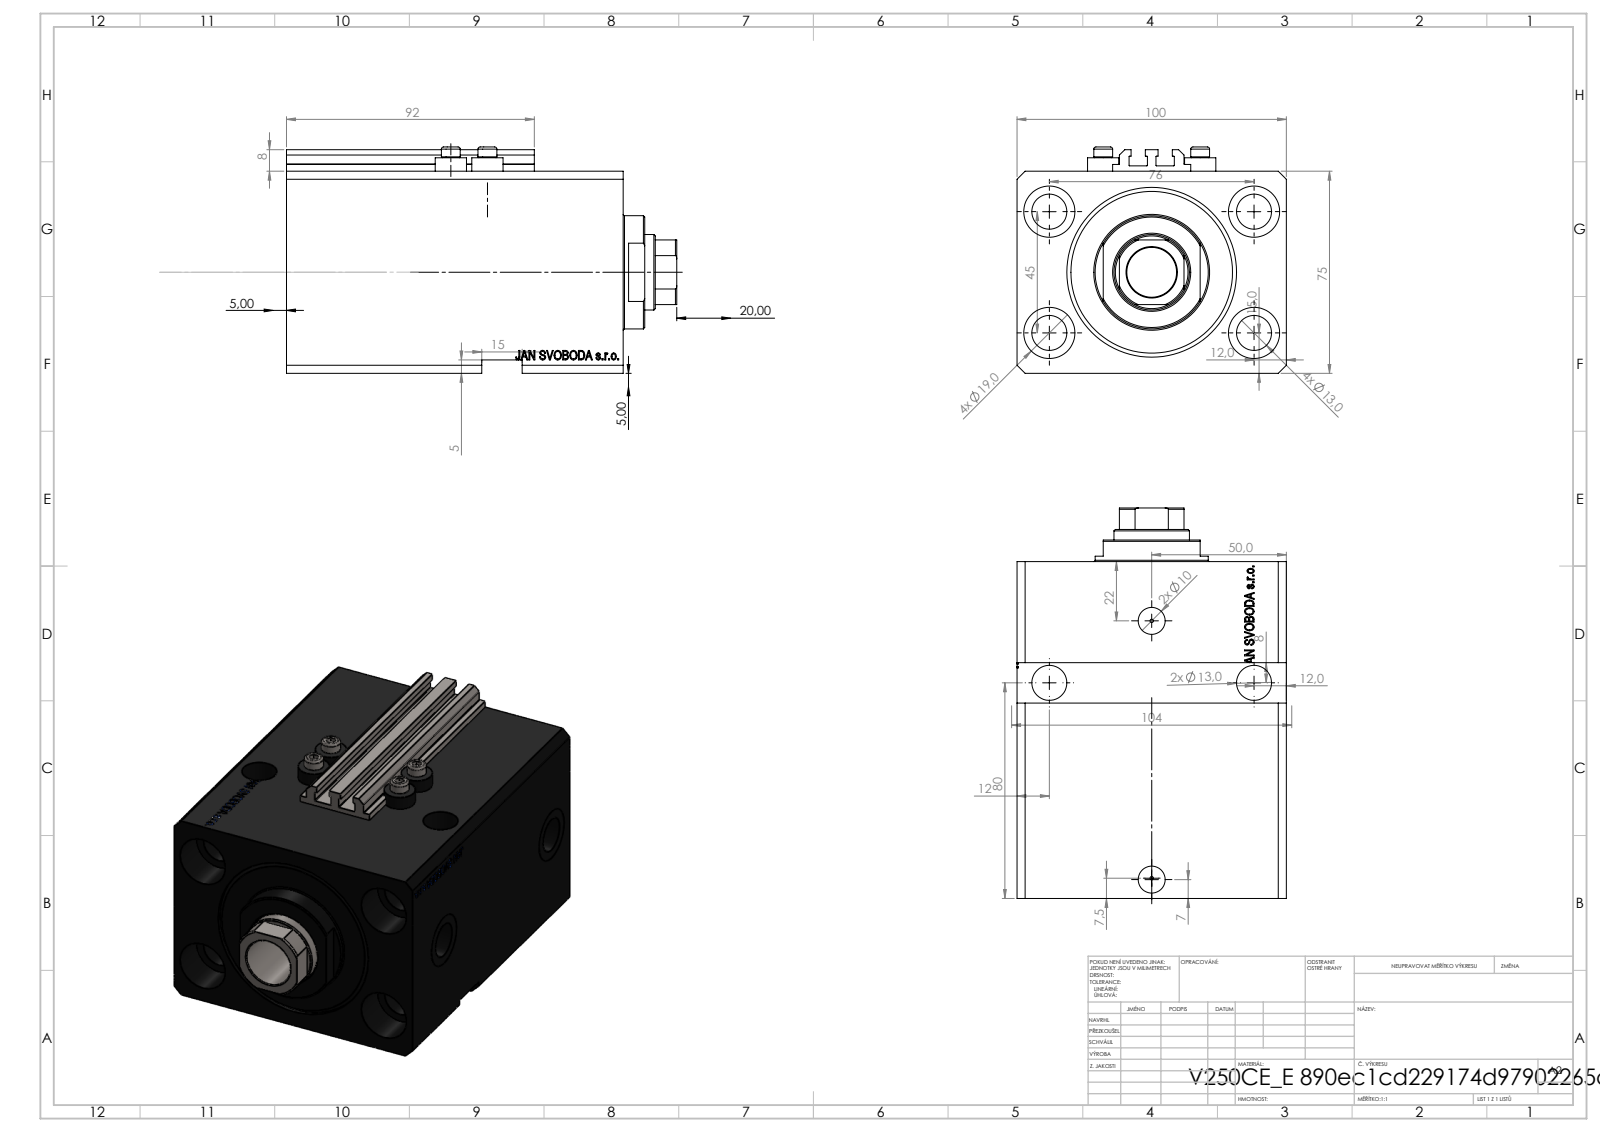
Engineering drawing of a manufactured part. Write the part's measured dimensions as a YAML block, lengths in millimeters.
part_name: "V250CE_E_Body; V250CE_C_VCP; ALLEN BOLT V250CE; V250CE_VC_E"
step_written_by: "SolidWorks 2019 (CONFIG_CONTROL_DESIGN)"
units: millimeters
bodies: {solids: 8, faces: 1108, planar: 535, cylindrical: 146, other: 427}
overall_size: [145, 100, 84]
volume: 768812
surface_area: 150350
round_holes:
  - {diameter: 13, count: 8}
  - {diameter: 1.25, count: 4}
  - {diameter: 4, count: 4}
  - {diameter: 19, count: 4}
  - {diameter: 10, count: 2}
  - {diameter: 13.16, count: 2}
  - {diameter: 20, count: 2}
  - {diameter: 18.5, count: 1}
  - {diameter: 28, count: 1}
  - {diameter: 50, count: 1}
  - {diameter: 63, count: 1}
round_bosses_or_shafts:
  - {diameter: 11.6, count: 4}
  - {diameter: 7, count: 4}
  - {diameter: 42, count: 1}
partial_cylinders:
  - {radius: 0.2, count: 10}
  - {radius: 13.5, count: 1}
face_to_face_distances: [75, 100, 125, 20, 11.9, 113.1, 105, 93.1, 70, 5]
hole_center_spacings: [44.16, 76, 13.6, 20.72, 27.59, 29, 33.62, 36]
